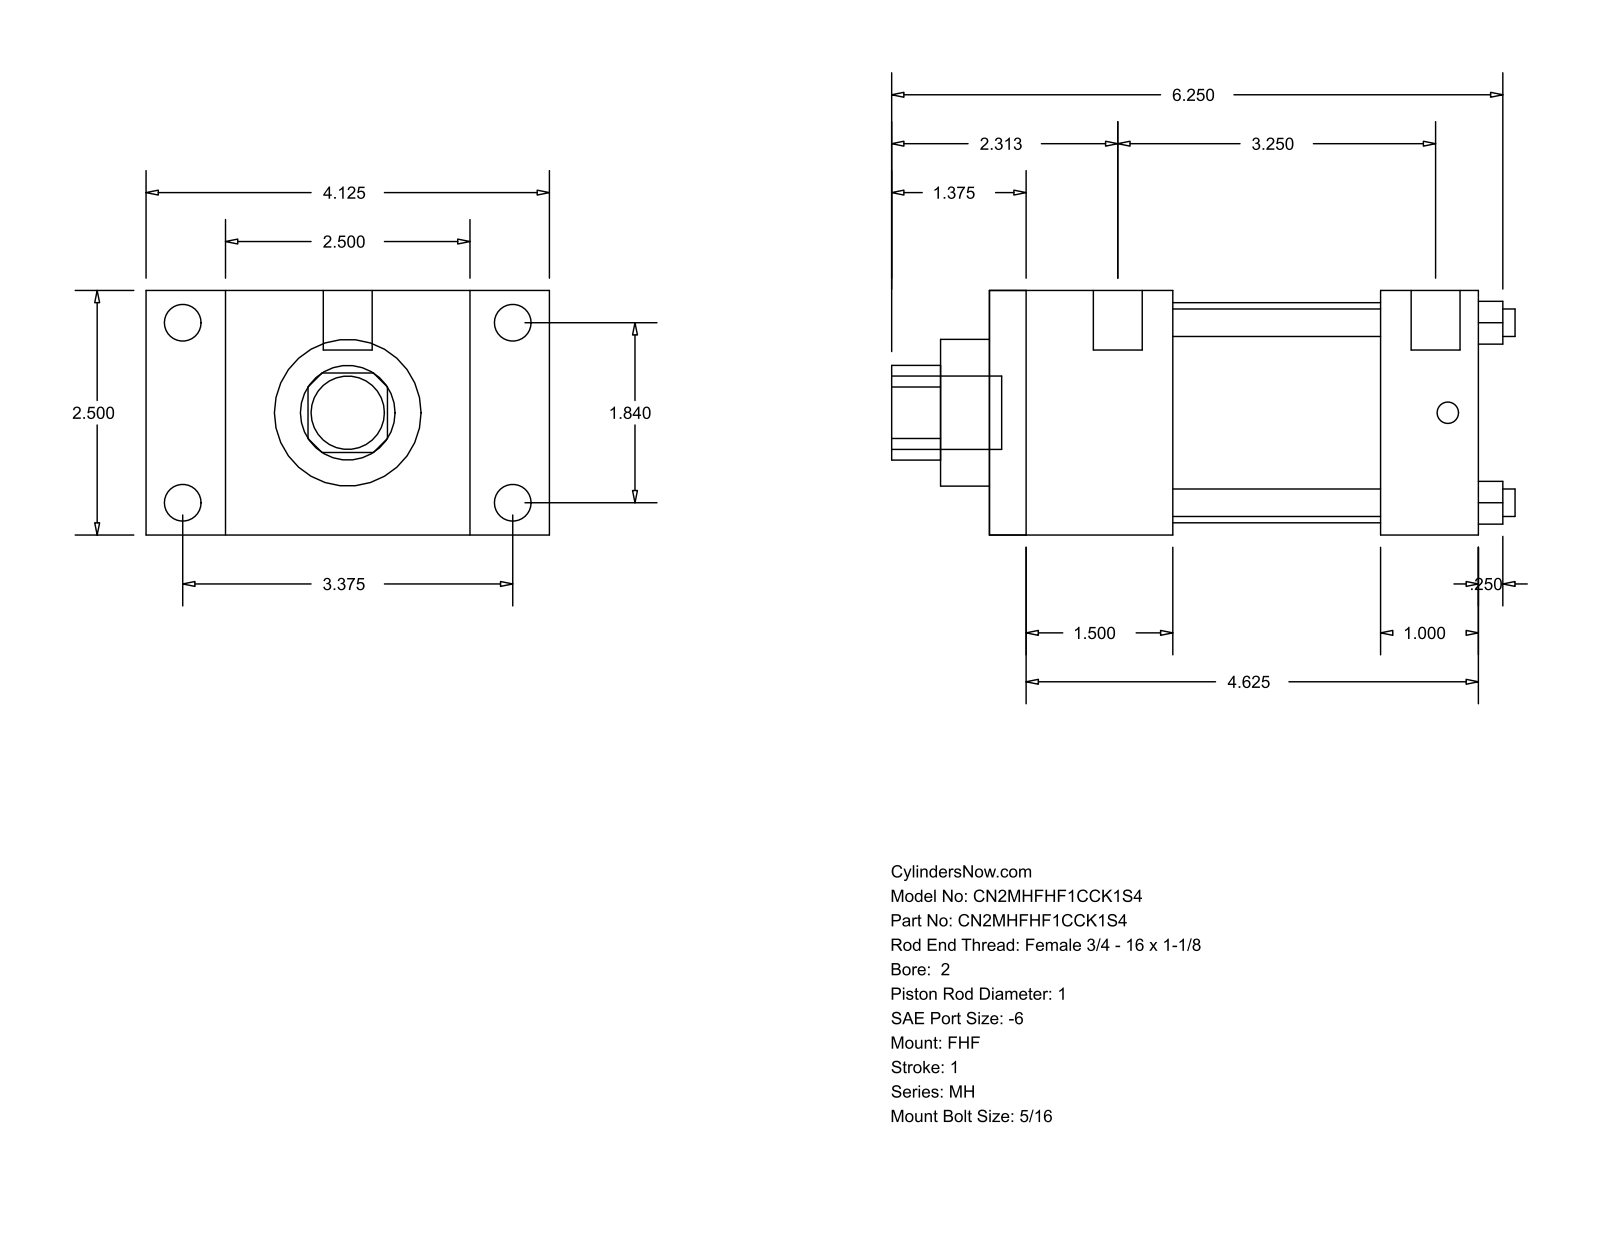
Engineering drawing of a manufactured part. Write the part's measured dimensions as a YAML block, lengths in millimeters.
part_name: "MH_FHF__0200_1"
step_written_by: "GSSL Pune (CONFIG_CONTROL_DESIGN)"
units: millimeters
bodies: {solids: 0, faces: 88, planar: 60, cylindrical: 28, other: 0}
overall_size: [161.93, 104.78, 63.5]
round_holes:
  - {diameter: 7.14, count: 4}
  - {diameter: 25.4, count: 1}
  - {diameter: 38.1, count: 1}
  - {diameter: 57.15, count: 1}
round_bosses_or_shafts:
  - {diameter: 9.53, count: 4}
  - {diameter: 5.56, count: 4}
  - {diameter: 12.7, count: 2}
  - {diameter: 19.05, count: 1}
partial_cylinders:
  - {radius: 12.29, count: 1}
face_to_face_distances: [63.5, 127, 47.63, 79.37, 20.64, 84.14, 104.78, 25.4, 101.6, 53.97]
hole_center_spacings: [33.05, 46.74, 66.1]
